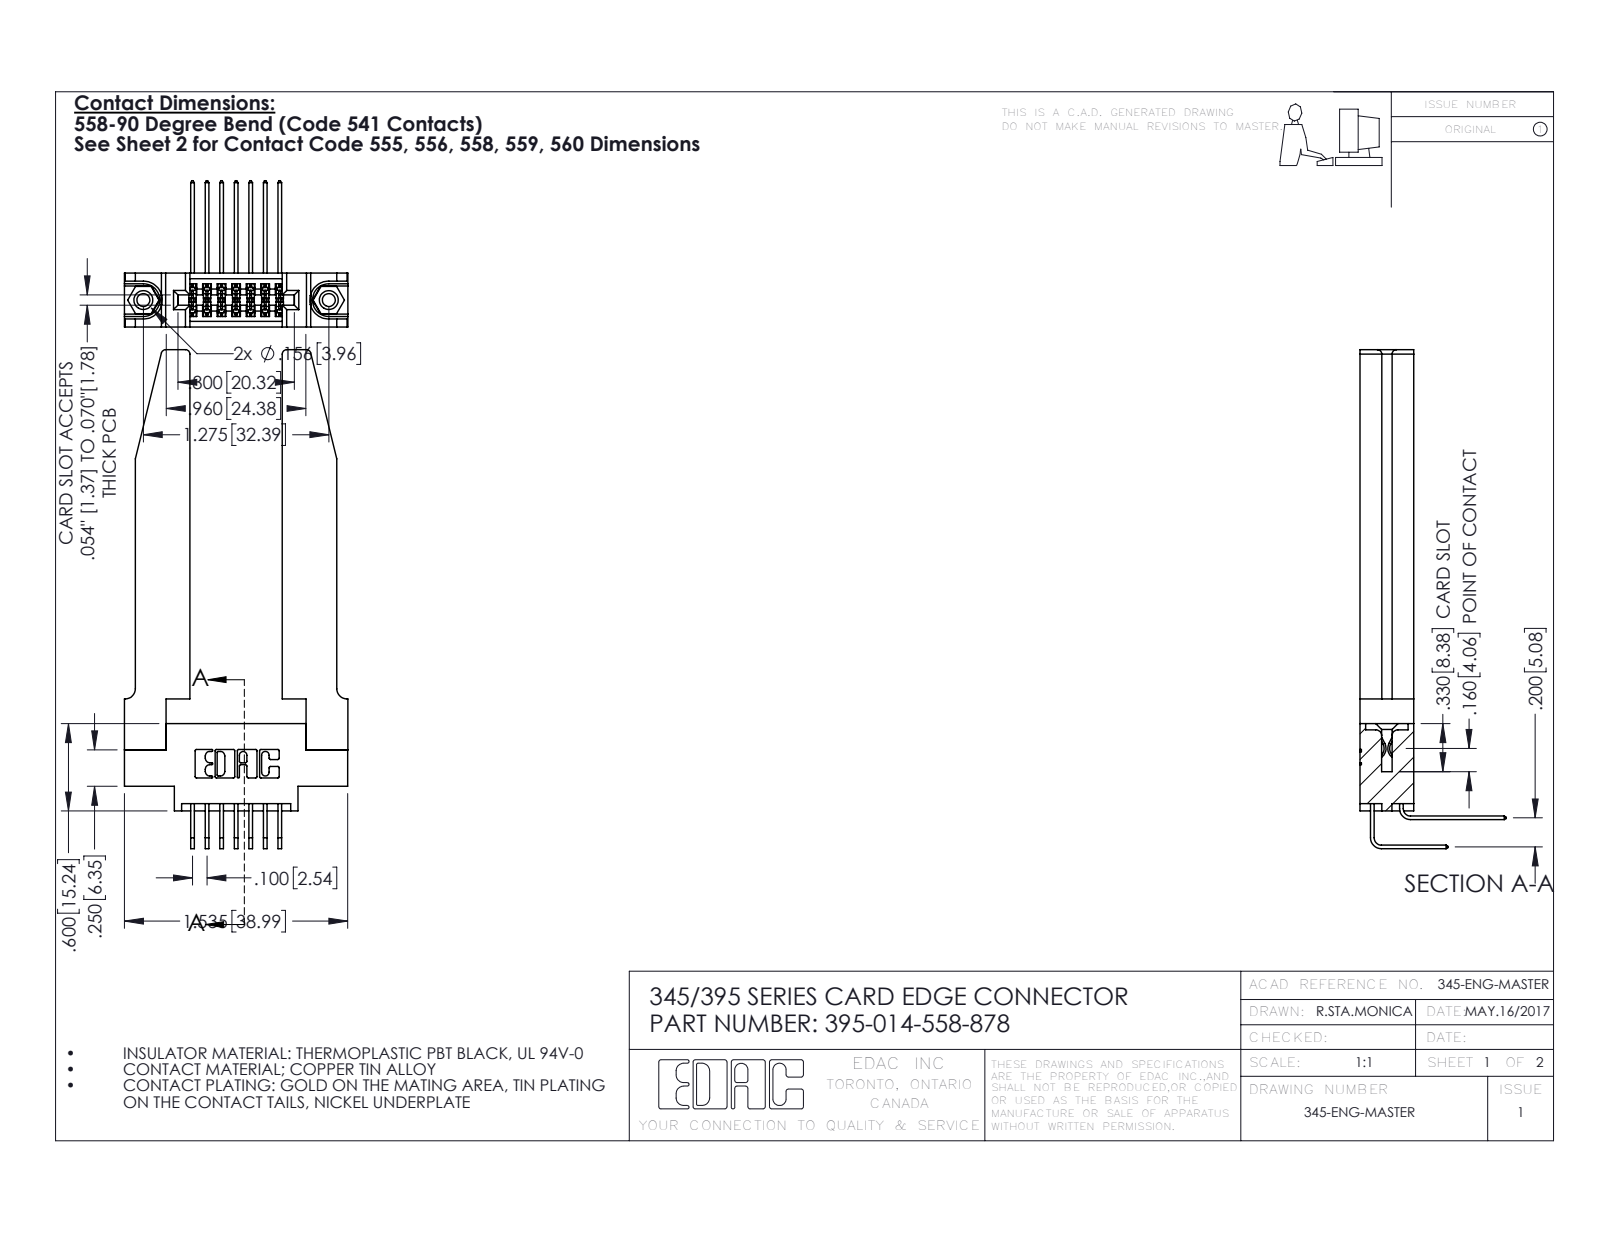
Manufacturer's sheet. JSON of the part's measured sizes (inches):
{"part_name": "345 Part_0.170 Offset - 0.156 Dia-TH; 345-292-001_558 559 Tail - 1; 345-220-078_345-220-078; 345-250-001_345-250-001-102 (+2 more)", "step_written_by": "SolidWorks 2016 (CONFIG_CONTROL_DESIGN)", "units": "inches", "bodies": {"solids": 19, "faces": 1092, "planar": 716, "cylindrical": 324, "other": 52}, "overall_size": [3.429, 1.536, 1.005], "volume_in3": 0.684, "surface_area_in2": 18.22, "round_holes": [[0.089, 2], [0.125, 2], [0.156, 2], [0.064, 1]], "round_bosses_or_shafts": [[0.155, 2]], "partial_cylinders_radius": [[0.006, 22], [0.01, 22], [0.03, 8], [0.007, 6], [0.031, 6], [0.026, 3], [0.014, 2], [0.019, 2]], "face_to_face_distances": [0.37, 0.15, 0.072, 0.148, 0.22, 0.298, 0.077, 0.635, 0.2, 0.095], "hole_center_spacings": [0.27, 1.045, 1.275]}
